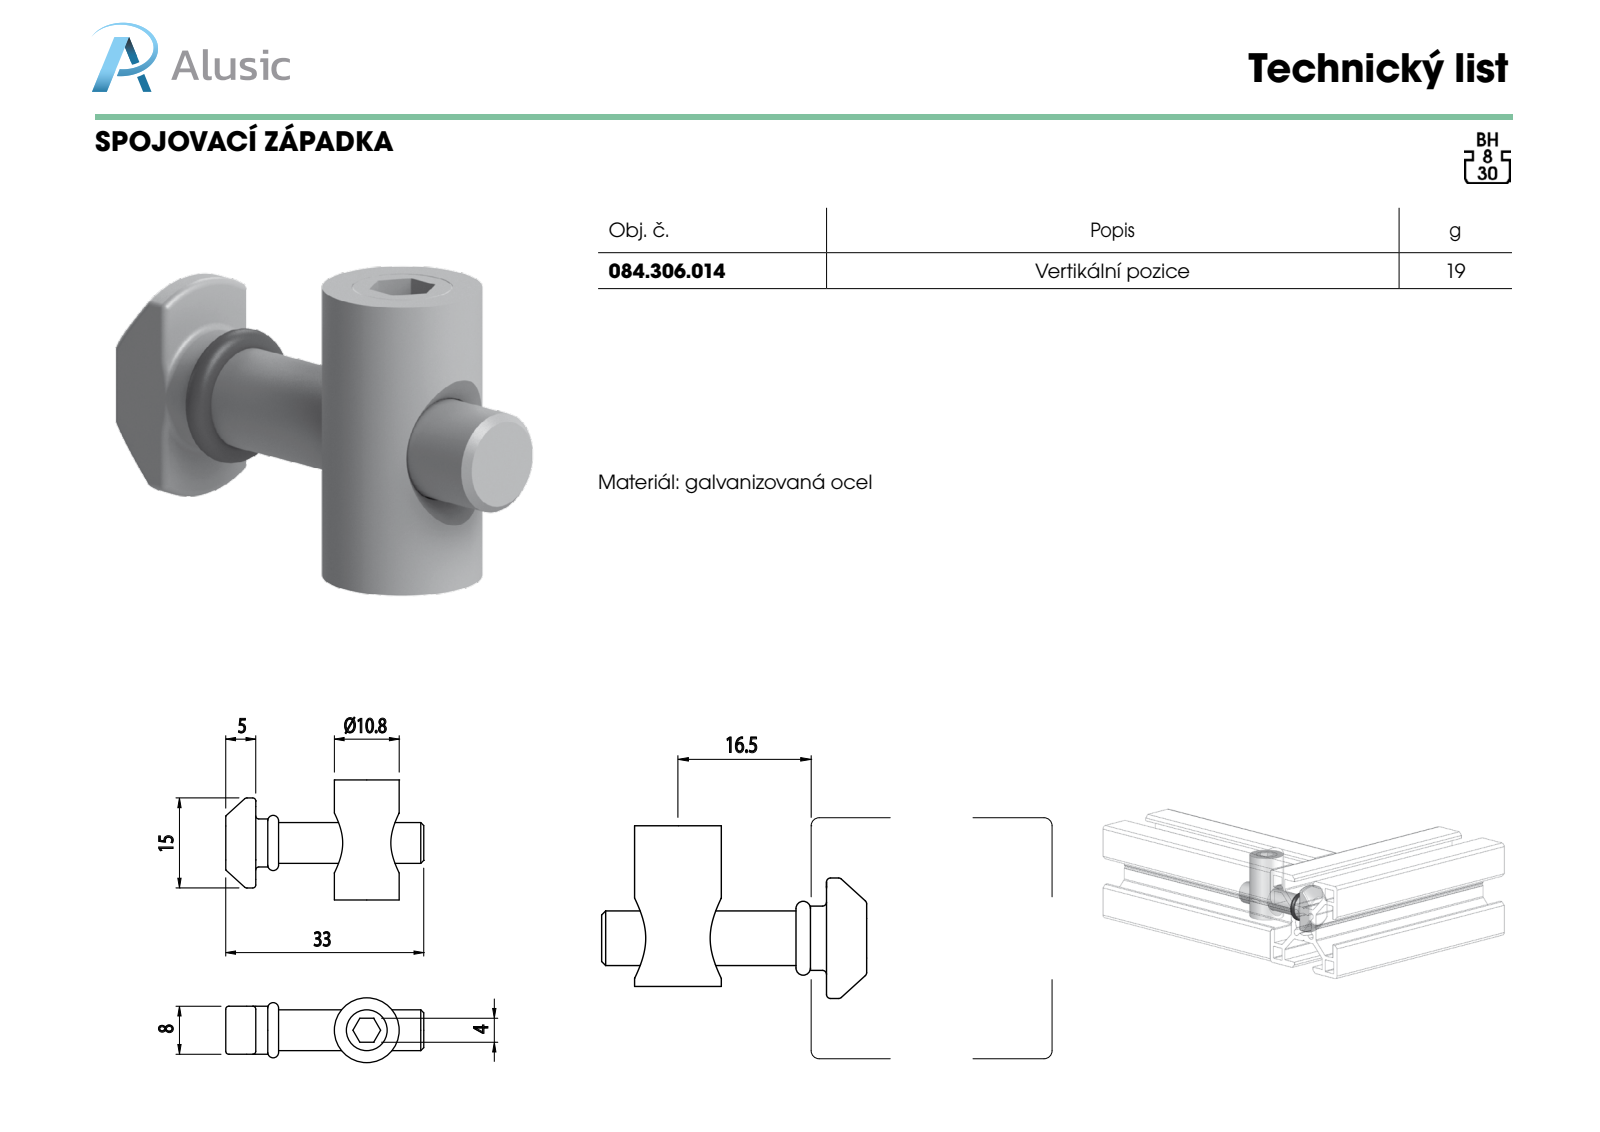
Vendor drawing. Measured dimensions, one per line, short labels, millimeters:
name: 084.306.014; Socket Set Screw Cone Point_ALUSIC_PreviewCfg; O-rings series A_ALUSIC_O-ring 5.6x1.8-A-ISO 3601-1; 3.JNT.003B (+1 more)
written by: SolidWorks 2012 (CONFIG_CONTROL_DESIGN)
unit: mm
bodies: 4 solids, 145 faces (18 planar, 41 cylindrical, 86 other)
size: 33 × 20 × 10.8
volume: 2 875 mm³; area: 2 740 mm²
holes: 1× ⌀6.8, 1× ⌀7
bosses: 2× ⌀8, 1× ⌀10.8, 1× ⌀6.8, 1× ⌀5.4
rounds: 8× R0.5, 1× R7.5
face distances: 20, 5, 8, 4, 7, 2, 33, 28, 26, 15
